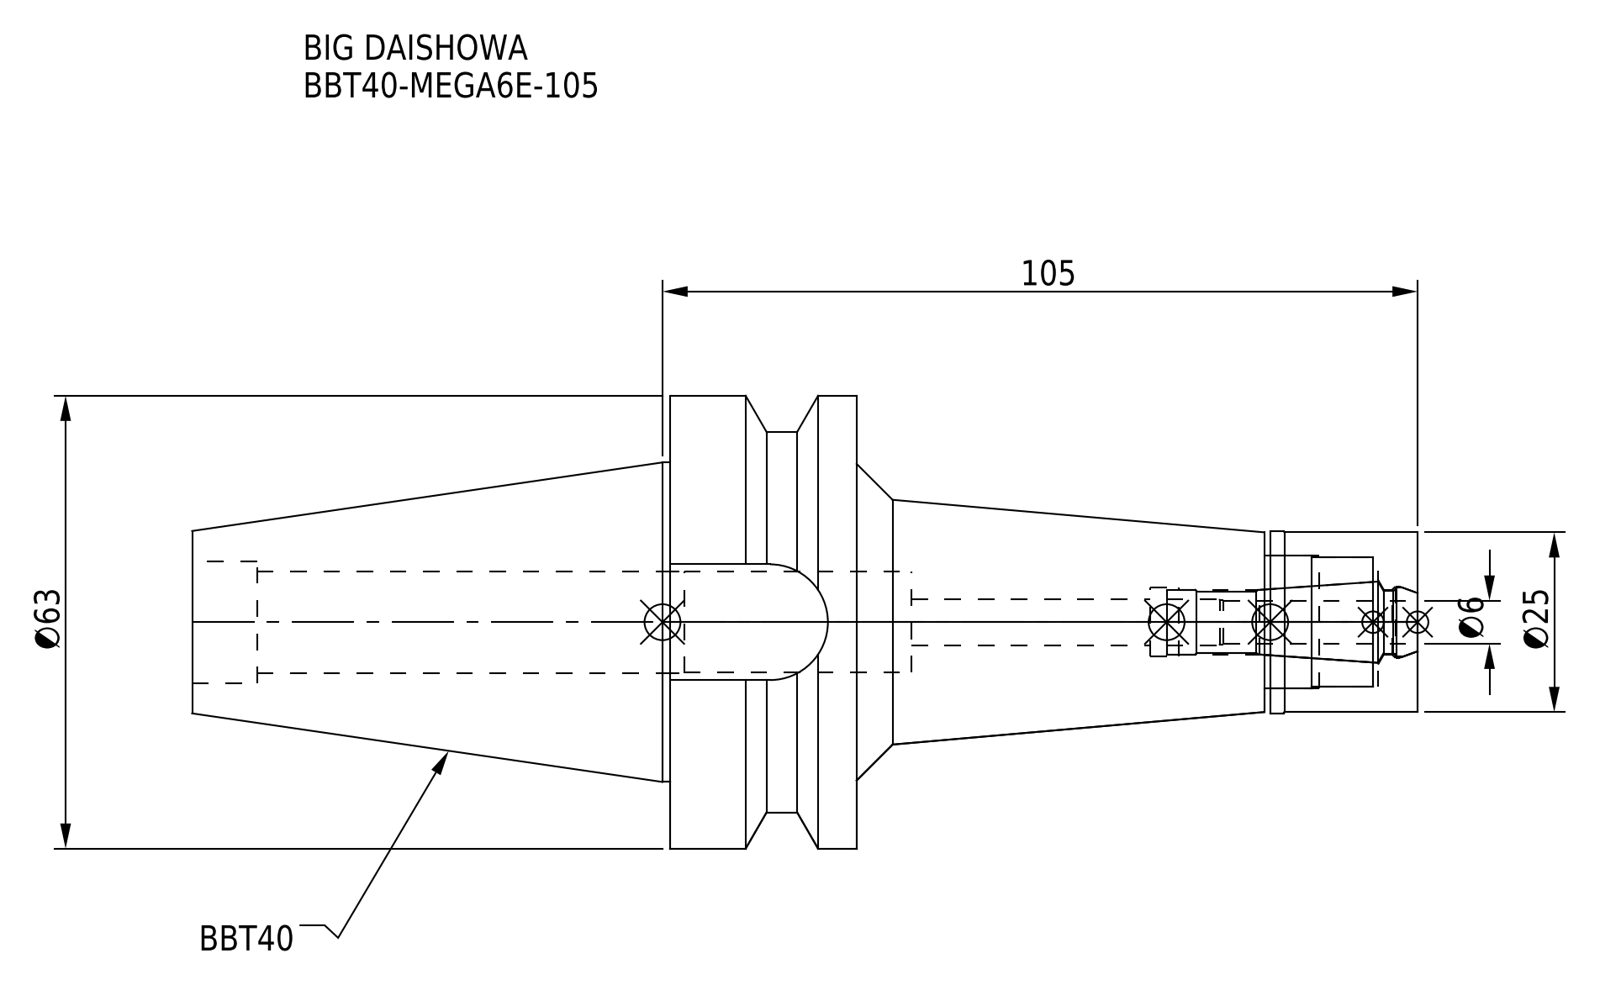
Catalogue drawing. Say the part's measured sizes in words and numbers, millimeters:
The part is named "DXF_TEMP_ASSY_ASM_4_ASM.stp; BBT40-MEGA6E-105; MEN6_1.stp; BBT40-MEGA6E-105_1.stp (+3 more)". Its 3-D file was written by "SolidWorks 2019 (CONFIG_CONTROL_DESIGN)". It is 2 solids with 81 faces: 21 planar, 40 cylindrical and 20 other. Overall it measures 170.4 by 63 by 63 millimeters. Its volume is 167 344 cubic millimeters and its surface area 33 876 square millimeters. Round holes: 1 of diameter 6.4, 1 of diameter 9, 1 of diameter 9.6, 1 of diameter 9.9, 1 of diameter 14, 1 of diameter 14.2, 1 of diameter 17, 1 of diameter 18, 1 of diameter 18.5. Round bosses or shafts: 1 of diameter 63, 1 of diameter 53, 1 of diameter 44.45, 1 of diameter 25.3, 1 of diameter 25. Partial cylindrical surfaces (rounded edges, fillets, slot ends): 1 of radius 8.05. The main face-to-face distances are 26, 78, 104, 45, 170.4, 92.4, 66.4, 56.7, 20.5, 57.5.
